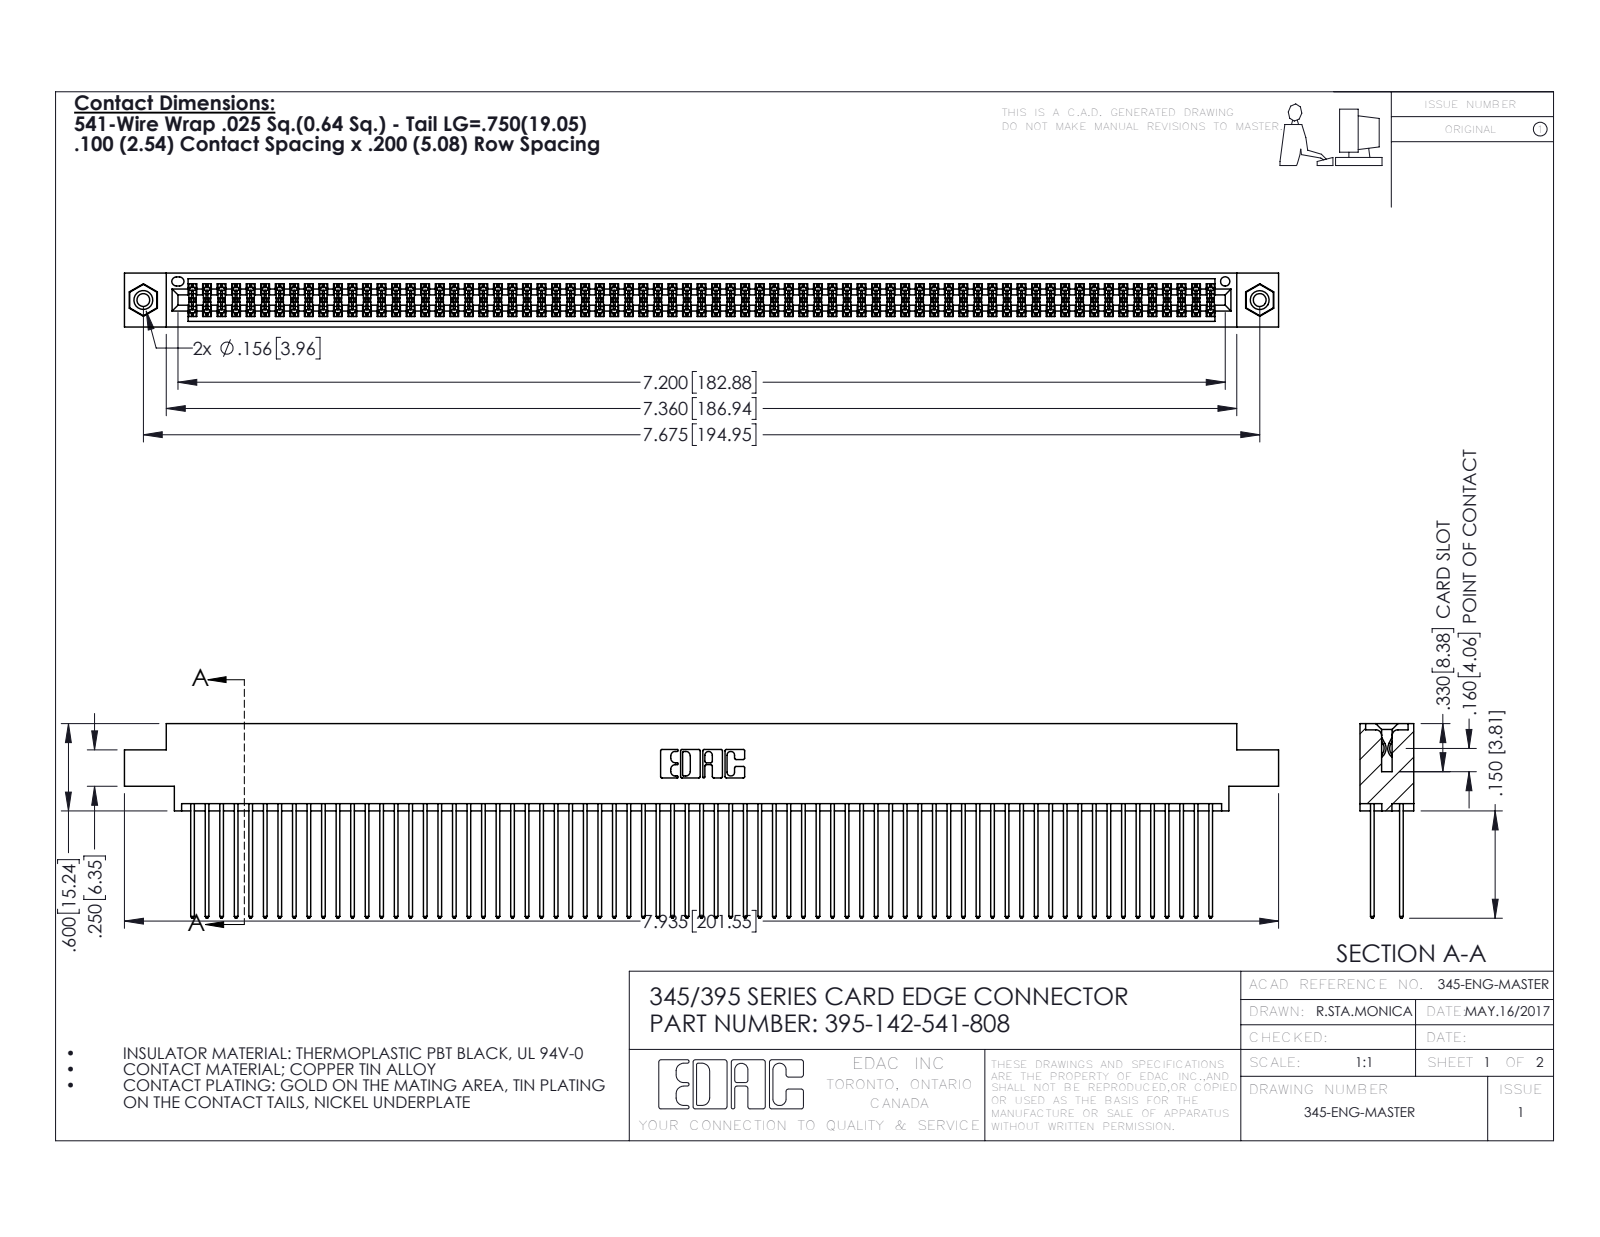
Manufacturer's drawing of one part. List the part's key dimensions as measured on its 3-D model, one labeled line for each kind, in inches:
Part name (STEP PRODUCT): 345-292-001_345-293-141; 345 Part_0.170 Offset - 0.156 Dia-TI; 395-142-541-808; 345-250-001_345-250-003-102
STEP written by: SolidWorks 2016 (CONFIG_CONTROL_DESIGN)
Units: inches
Bodies: 145 solids, 7290 faces (4802 planar, 2472 cylindrical, 16 other)
Overall size (bounding box): 7.935 × 1.337 × 0.37
Volume: 1.254 in³ · Surface area: 54.12 in²
Round holes (diameter × count): ⌀0.089 ×2, ⌀0.125 ×2, ⌀0.156 ×2, ⌀0.064 ×1
Round bosses / shafts (diameter × count): ⌀0.155 ×2
Partial cylindrical surfaces — rounded edges, fillets, slot ends (radius × count): R0.006 ×213, R0.01 ×142, R0.01 ×22, R0.007 ×6, R0.031 ×6, R0.026 ×3, R0.014 ×2, R0.019 ×2
Main face-to-face distances: 0.072, 0.298, 0.2, 0.098, 0.272, 0.025, 0.225, 0.37, 0.175, 0.149
Hole centre spacings: 0.27, 7.439, 7.675
